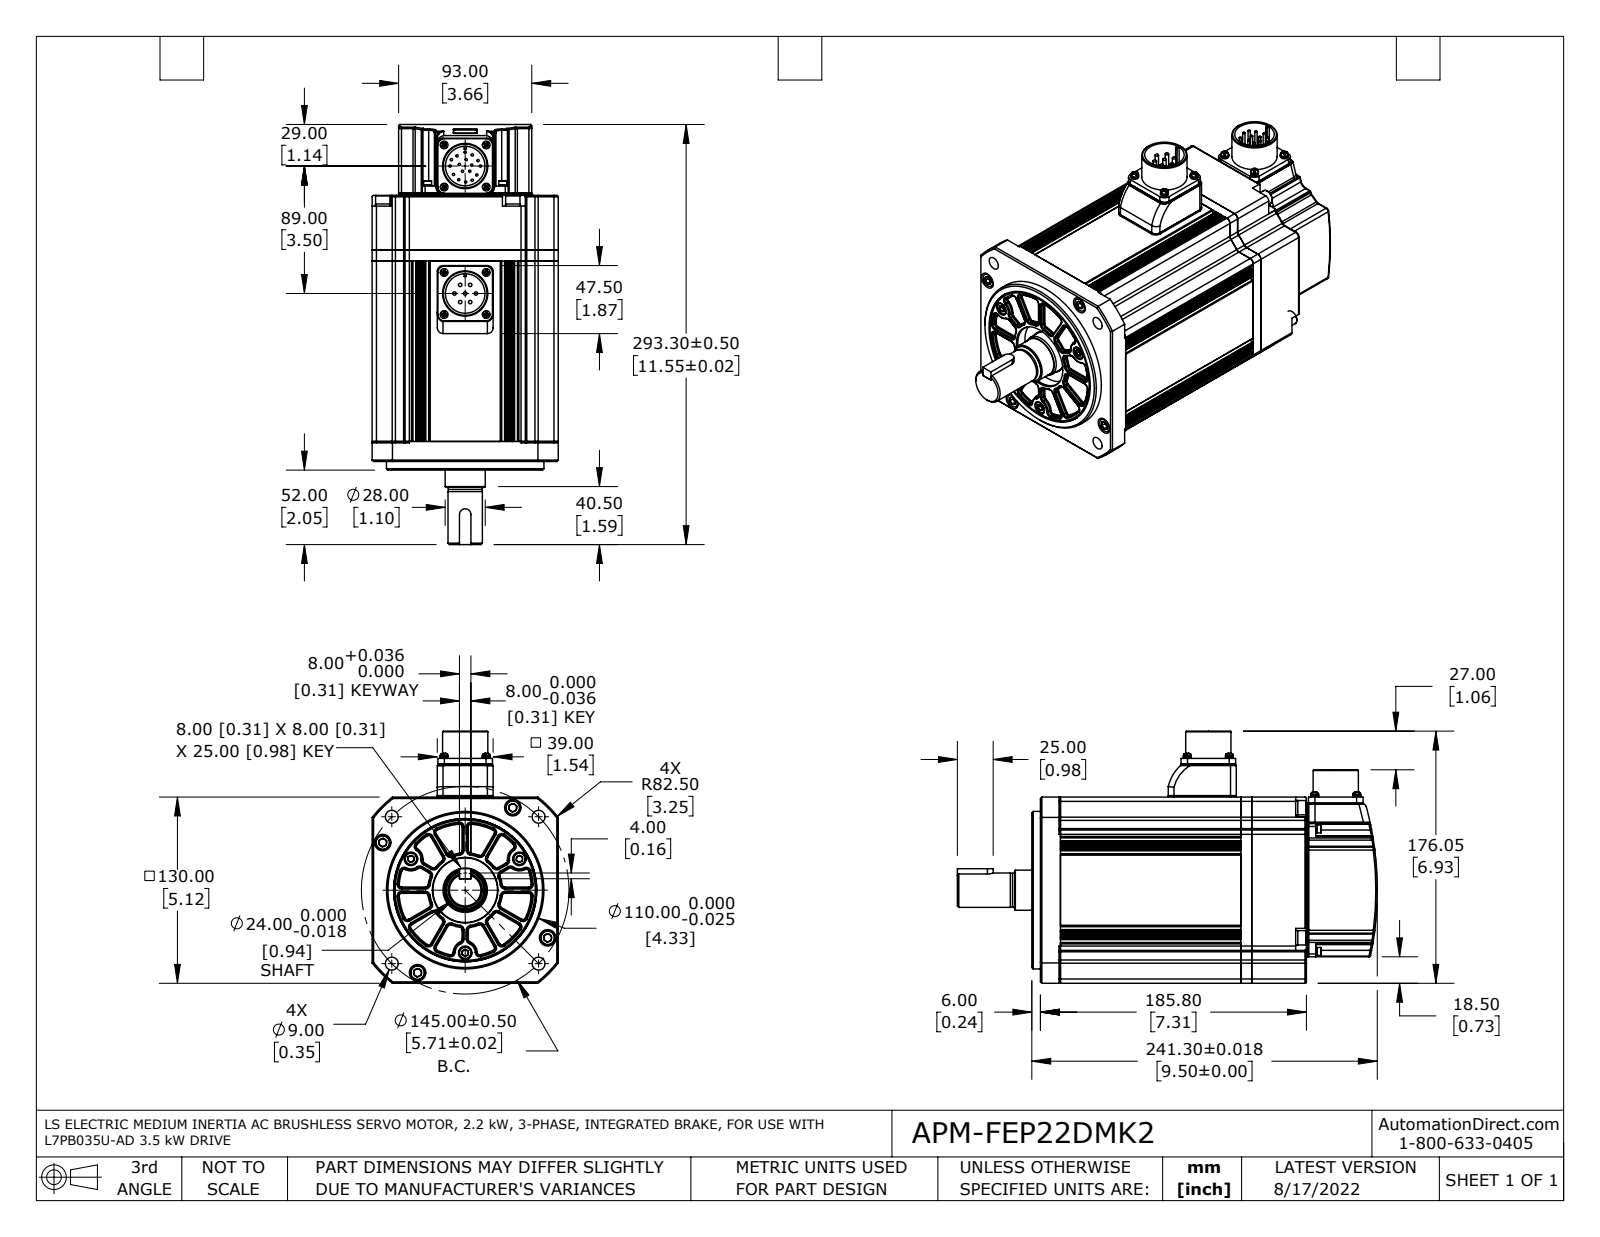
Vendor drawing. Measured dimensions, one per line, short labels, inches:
name: FMP13GA003G04_Out Line(APM-FEP22D_K2) r1 nc fxt
written by: SolidWorks 2017 (AUTOMOTIVE_DESIGN)
unit: in
bodies: 57 solids, 2213 faces (729 planar, 843 cylindrical, 641 other)
size: 11.547 × 6.931 × 5.118
volume: 198.9 in³; area: 567.8 in²
holes: 12× ⌀0.098, 8× ⌀0.118, 8× ⌀0.12, 8× ⌀0.138, 7× ⌀0.197, 4× ⌀0.142, 4× ⌀0.146, 4× ⌀0.268, 4× ⌀0.276, 4× ⌀0.354, 4× ⌀0.453, 3× ⌀0.22
bosses: 17× ⌀0.063, 8× ⌀0.213, 7× ⌀0.094, 4× ⌀0.402, 4× ⌀0.394, 4× ⌀0.236, 4× ⌀0.217, 4× ⌀0.118
rounds: 72× R0.02, 54× R0.098, 24× R0.028, 22× R0.039, 17× R0.079, 16× R0.118, 12× R0.177, 9× R0.157
face distances: 4.961, 0.299, 5.26, 0.039, 5.118, 6.823, 0.906, 1.524, 1.823, 6.783
hole spacings: 0.819, 1.157, 3.504, 0.752, 1.041, 1.637, 1.975, 2.618
